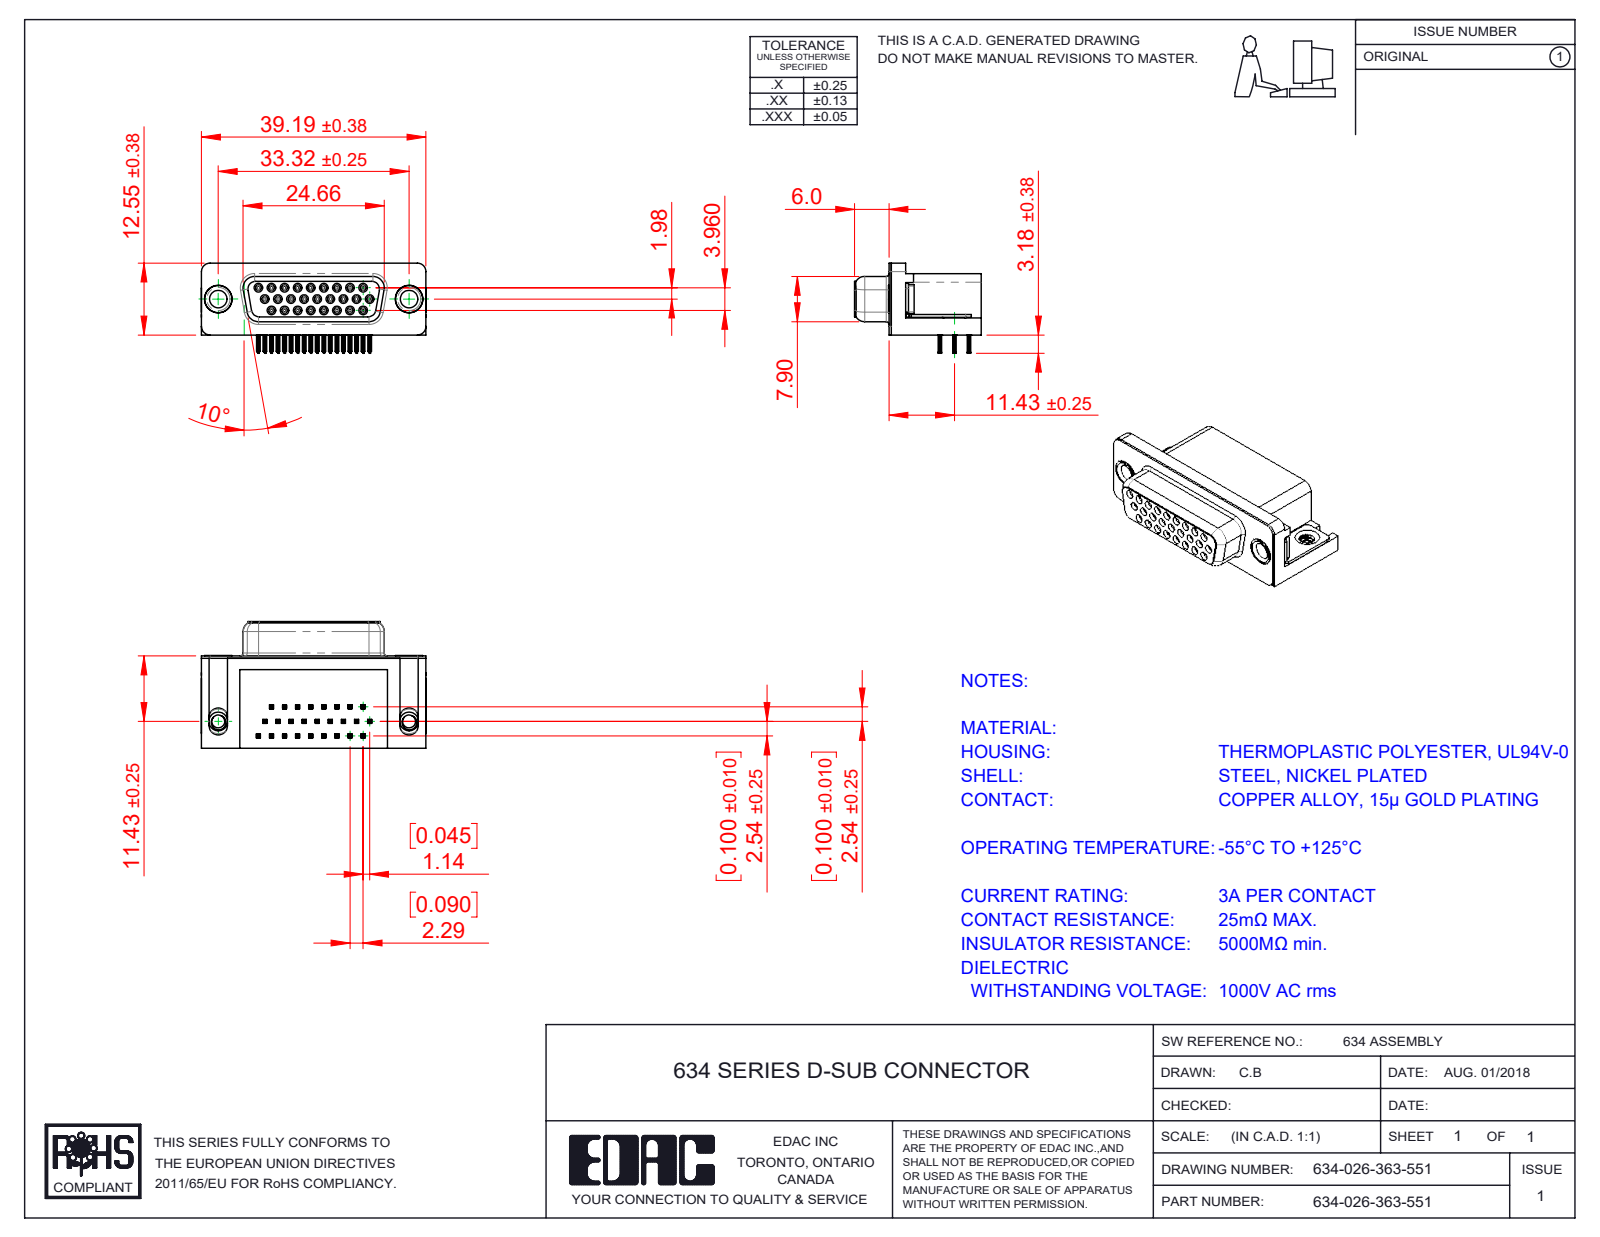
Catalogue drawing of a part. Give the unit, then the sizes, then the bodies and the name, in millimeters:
Units: millimetres
Overall size (bounding box): 39.22 × 22.1 × 16.25
Round holes (diameter × count): ⌀0.8 ×26, ⌀0.9 ×26, ⌀2 ×2, ⌀3.05 ×2, ⌀4 ×2, ⌀4.8 ×2, ⌀5 ×2
Round bosses / shafts (diameter × count): ⌀1.2 ×26, ⌀4.9 ×2, ⌀4.75 ×2, ⌀3.85 ×2, ⌀3 ×2
Partial cylindrical surfaces — rounded edges, fillets, slot ends (radius × count): R0.1 ×208, R0.15 ×104, R0.35 ×52, R0.34 ×26, R1 ×19, R0.25 ×12, R0.28 ×8, R1.35 ×8
Main face-to-face distances: 0.4, 10.34, 0.35, 15.7, 16.1, 6.65, 2.5, 0.85, 2.9, 10.69
Hole centre spacings: 2.29, 4.57, 2.28, 3.96, 6.05, 2.3, 2.27, 4.58
Volume: 6 364 mm³ · Surface area: 9 135 mm²
Bodies: 32 solids, 4061 faces (1813 planar, 926 cylindrical, 1322 other)
Part name (STEP PRODUCT): 634-026-363-551; Thru Hole Rivet; 634 Housing_26 Socket; Contact Middle (+4 more)
STEP written by: SolidWorks 2016 (CONFIG_CONTROL_DESIGN)
